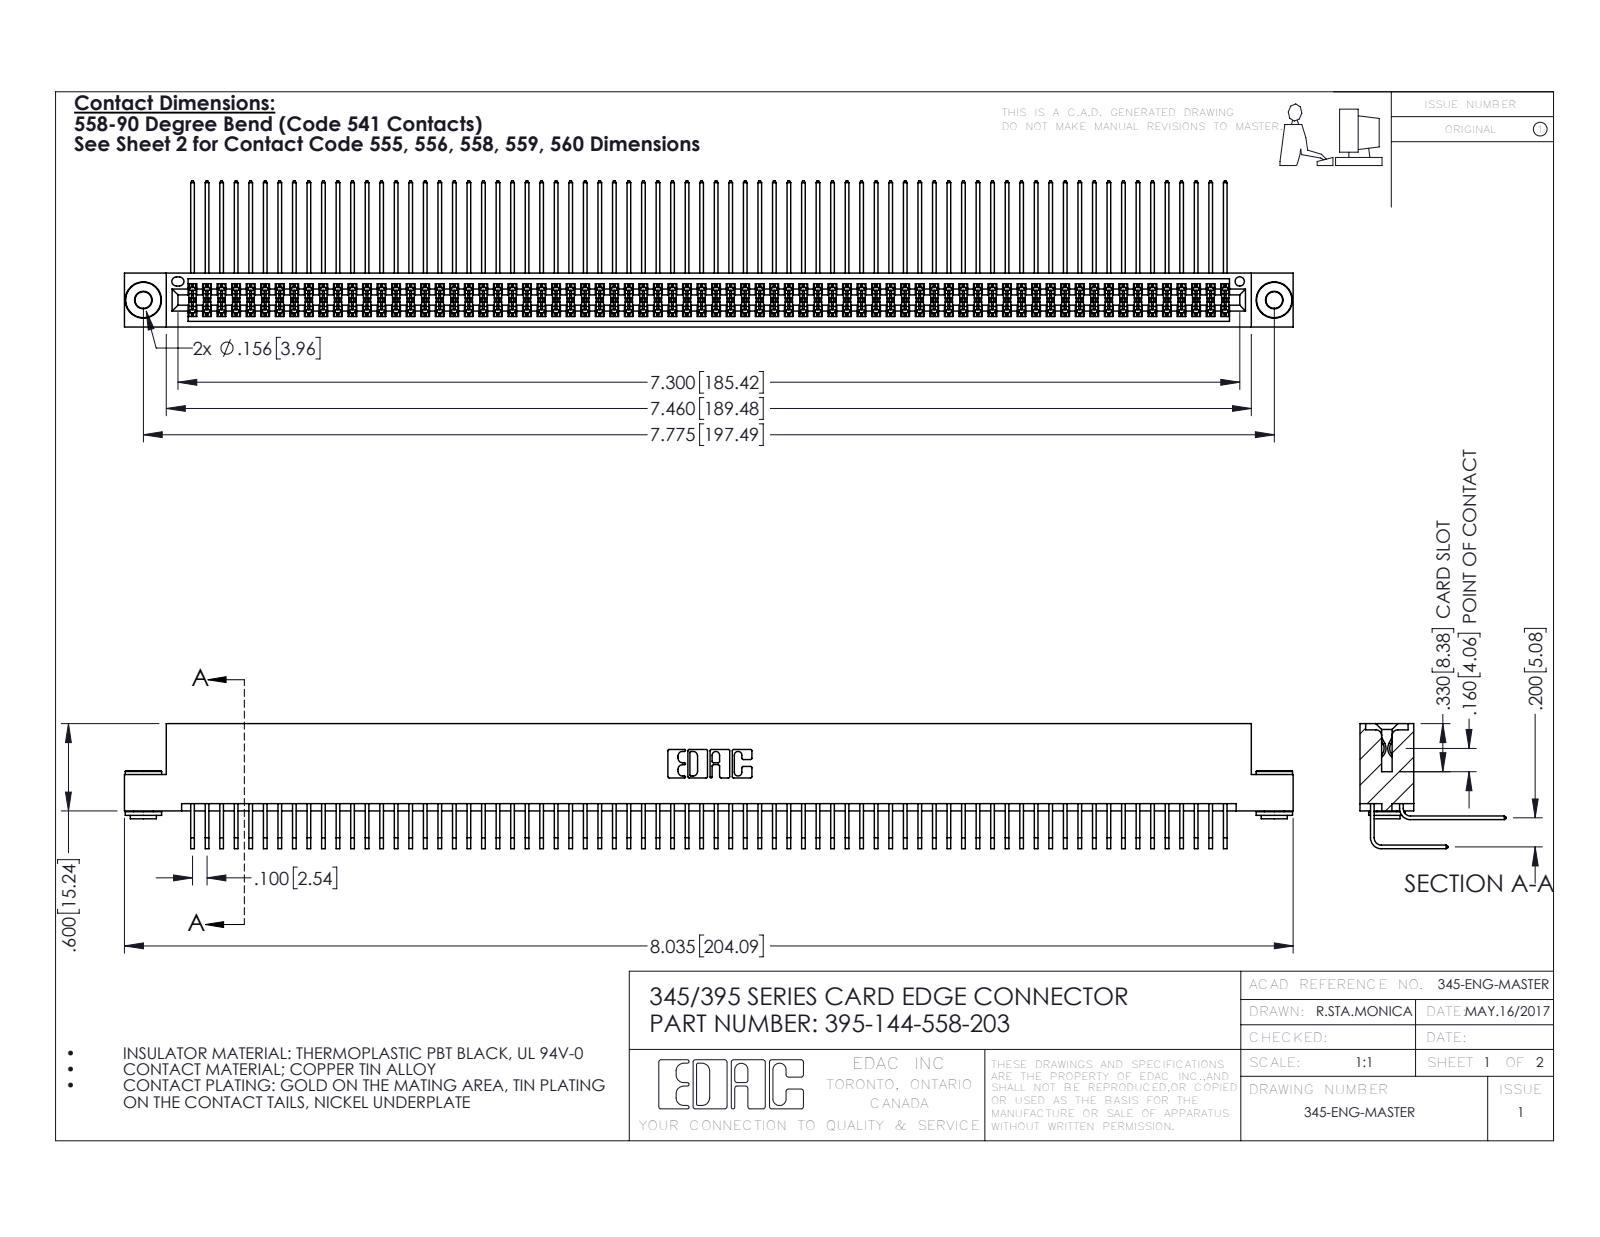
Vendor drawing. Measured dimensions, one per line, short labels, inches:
name: 345-292-001_558 Tail - 2; 395-144-558-203; 345 Part_Flush Mounting Lugs - 0.156 Dia-TH; 345-250-002_345-250-002-102 (+1 more)
written by: SolidWorks 2016 (CONFIG_CONTROL_DESIGN)
unit: in
bodies: 147 solids, 7652 faces (5130 planar, 2514 cylindrical, 8 other)
size: 8.035 × 1.005 × 0.859
volume: 1.279 in³; area: 55.28 in²
holes: 2× ⌀0.116, 2× ⌀0.156, 1× ⌀0.064
bosses: 2× ⌀0.25, 2× ⌀0.18, 2× ⌀0.136
rounds: 216× R0.006, 22× R0.01, 6× R0.007, 6× R0.031, 3× R0.026, 2× R0.014, 2× R0.019, 2× R0.022
face distances: 0.072, 0.298, 0.2, 0.37, 0.025, 0.098, 0.272, 0.225, 0.025, 0.175
hole spacings: 0.27, 7.539, 7.775
